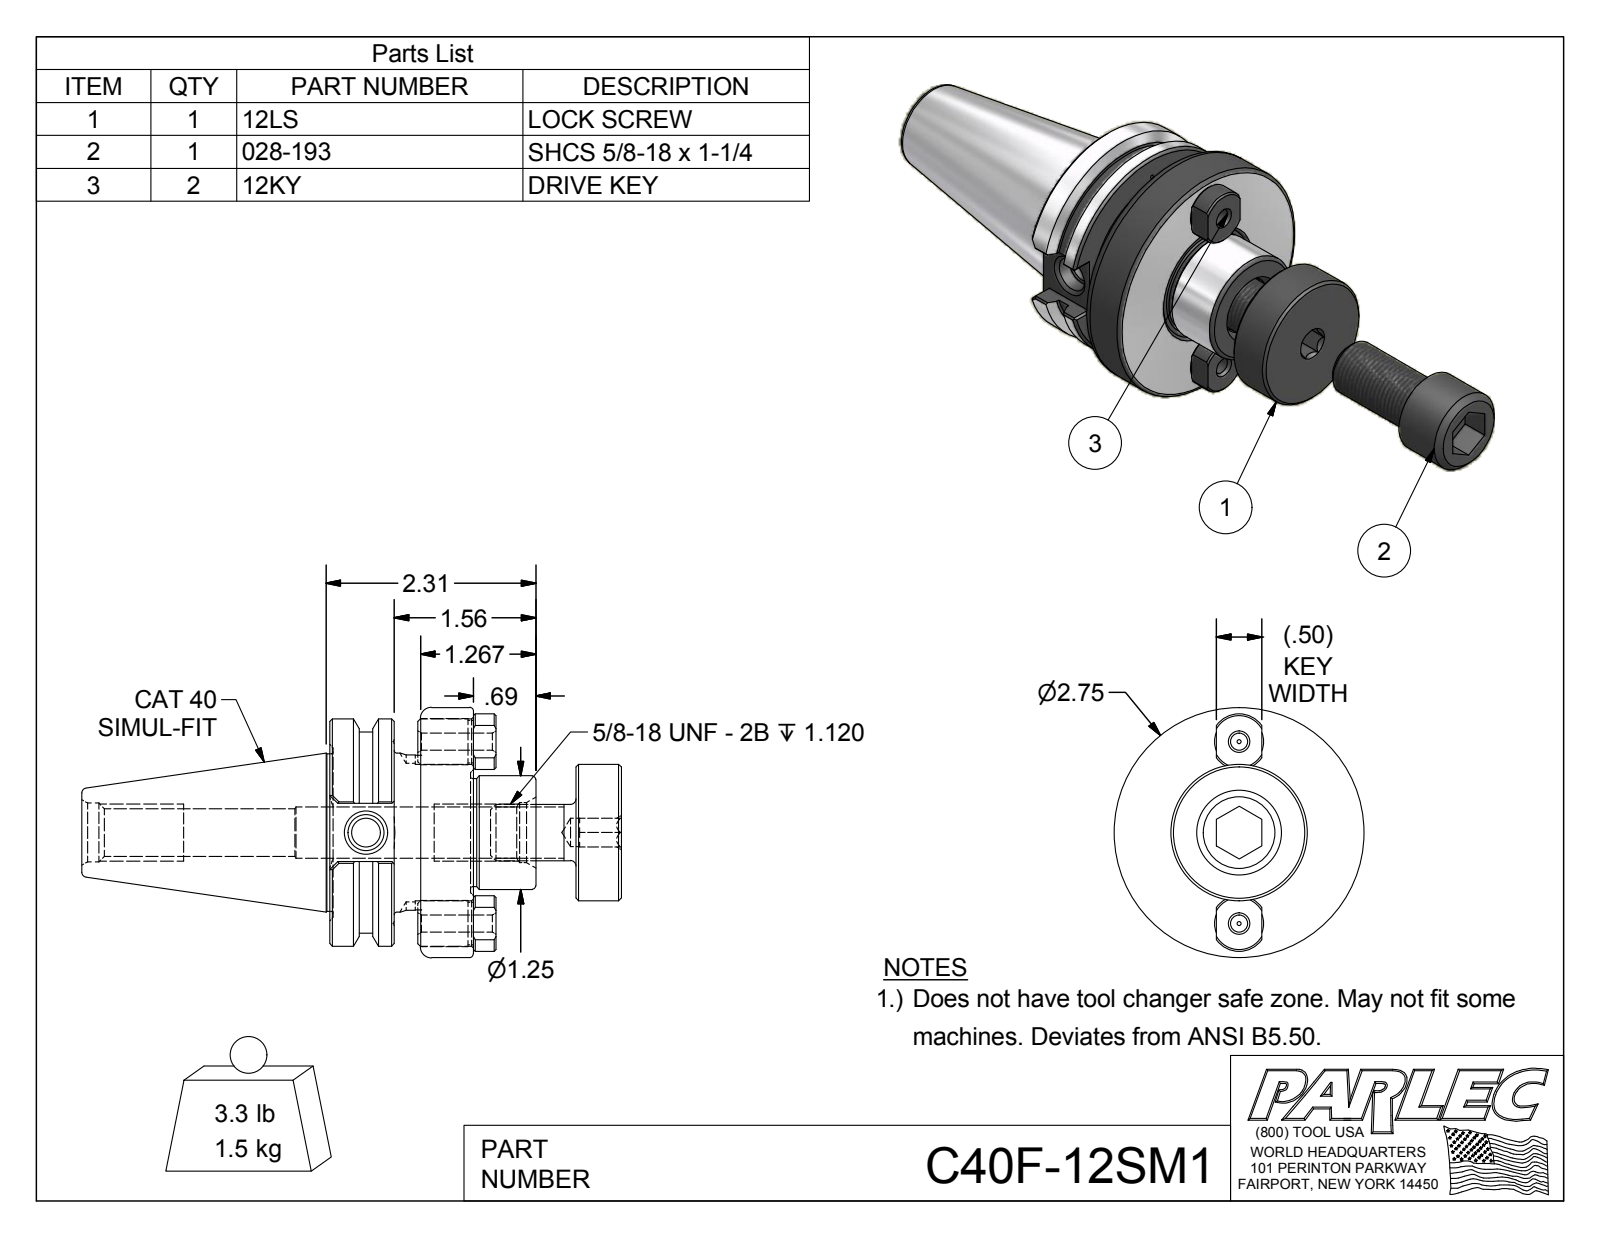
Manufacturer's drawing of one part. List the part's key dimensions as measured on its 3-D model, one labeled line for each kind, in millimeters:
Part name (STEP PRODUCT): C40F-12SM1; C40F-12SM1-1; 12KY; 028-193 (+1 more)
STEP written by: Autodesk Inventor 2012 (AUTOMOTIVE_DESIGN)
Units: millimetres
Bodies: 5 solids, 164 faces (69 planar, 36 cylindrical, 59 other)
Overall size (bounding box): 212.4 × 69.9 × 69.9
Volume: 208 100 mm³ · Surface area: 45 500 mm²
Round holes (diameter × count): ⌀4.8 ×2, ⌀12.7 ×2, ⌀7.9 ×1, ⌀8 ×1, ⌀10.1 ×1, ⌀13.4 ×1, ⌀14.4 ×1, ⌀16.5 ×1, ⌀16.8 ×1
Round bosses / shafts (diameter × count): ⌀12.8 ×2, ⌀11.9 ×2, ⌀69.9 ×1, ⌀63.5 ×1, ⌀56.3 ×1, ⌀44.5 ×1, ⌀43.9 ×1, ⌀38.1 ×1
Partial cylindrical surfaces — rounded edges, fillets, slot ends (radius × count): R6.1 ×2, R7.8 ×2
Main face-to-face distances: 14.7, 7.4, 22.1, 12.7, 63.4, 56.1, 41.3, 18.1, 25.4, 40.2
Hole centre spacings: 25.4, 50.8
